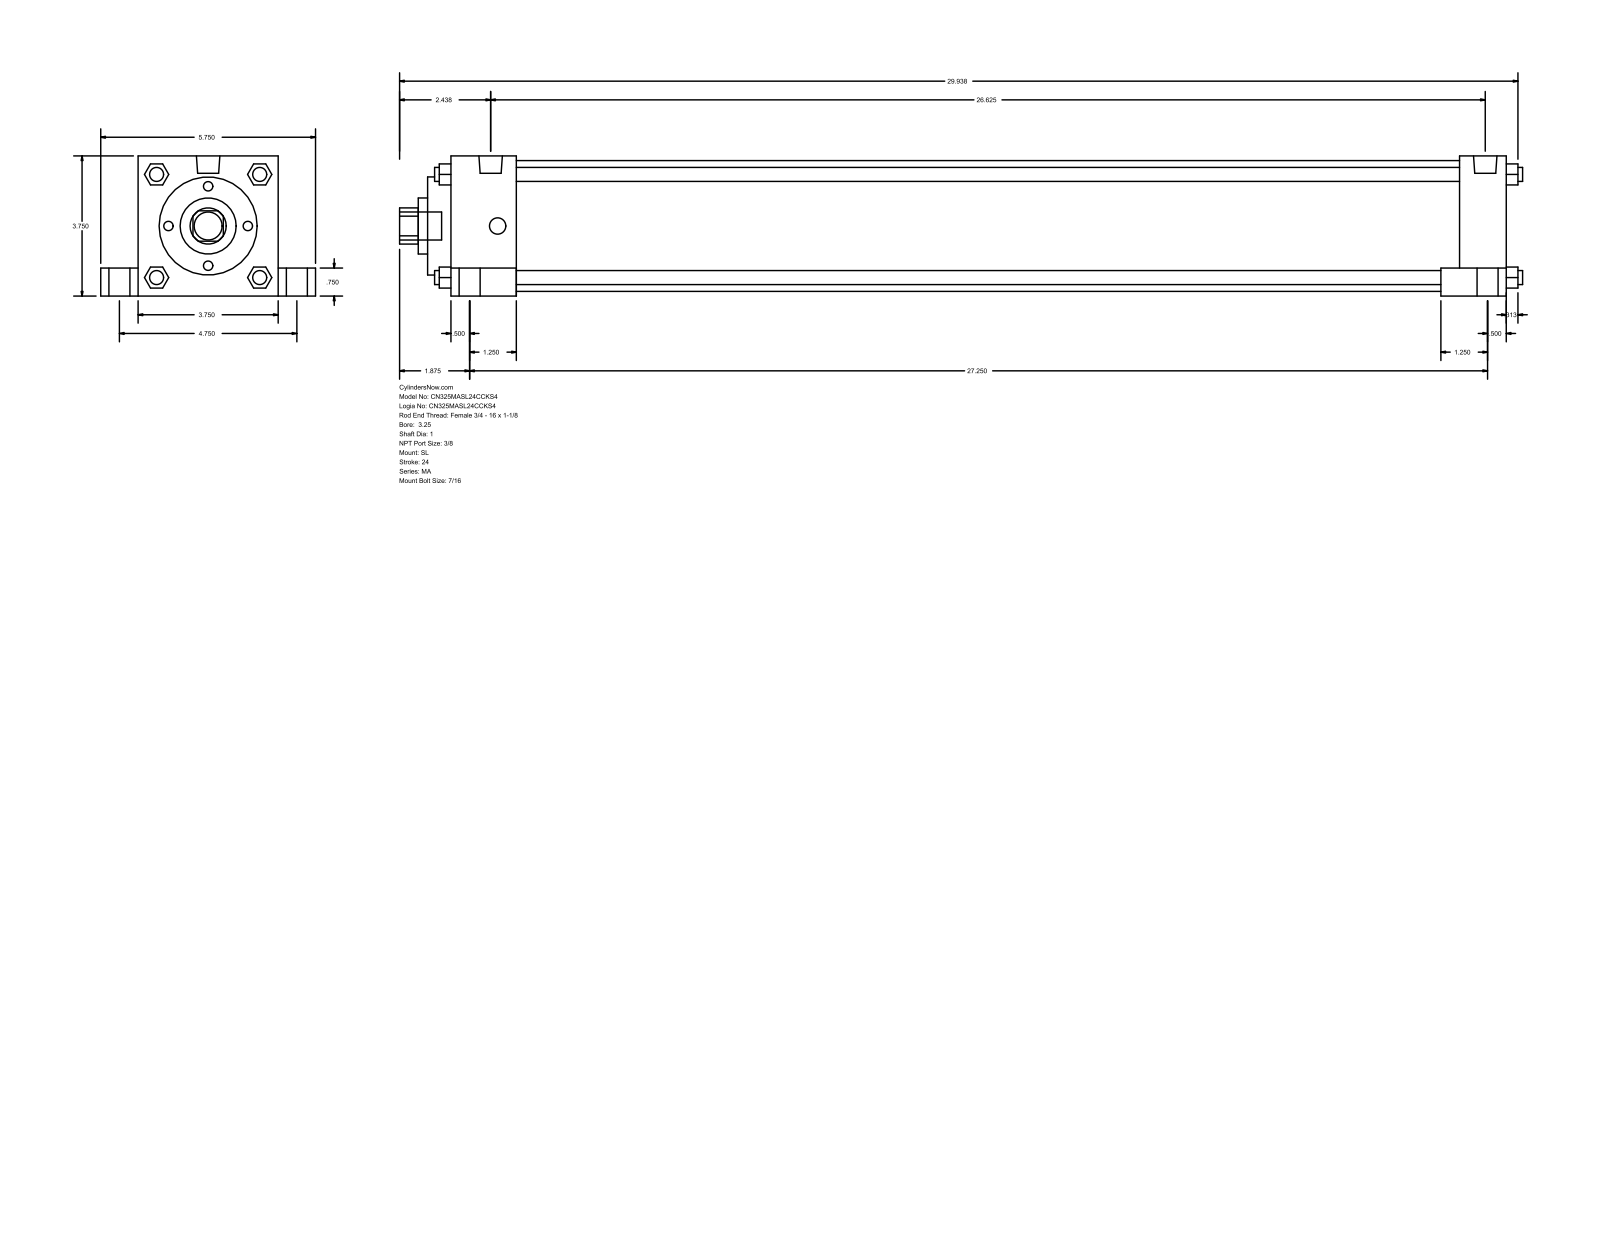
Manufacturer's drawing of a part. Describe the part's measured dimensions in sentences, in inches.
The part is named "MA_SL__0325_1". Its 3-D file was written by "GSSL Pune (CONFIG_CONTROL_DESIGN)". It is 0 solids with 150 faces: 113 planar, 37 cylindrical and 0 other. Overall it measures 30.063 by 5.75 by 3.75 inches. Round holes: 1 of diameter 1, 1 of diameter 1.5, 1 of diameter 2.625, 1 of diameter 3.5. Round bosses or shafts: 4 of diameter 0.813, 4 of diameter 0.563, 4 of diameter 0.437, 4 of diameter 0.375, 2 of diameter 0.627, 1 of diameter 0.75. Partial cylindrical surfaces (rounded edges, fillets, slot ends): 1 of radius 0.484. The main face-to-face distances are 3.75, 28.25, 25.25, 0.625, 1, 4.75, 0.75, 27, 1.25, 1.75.
